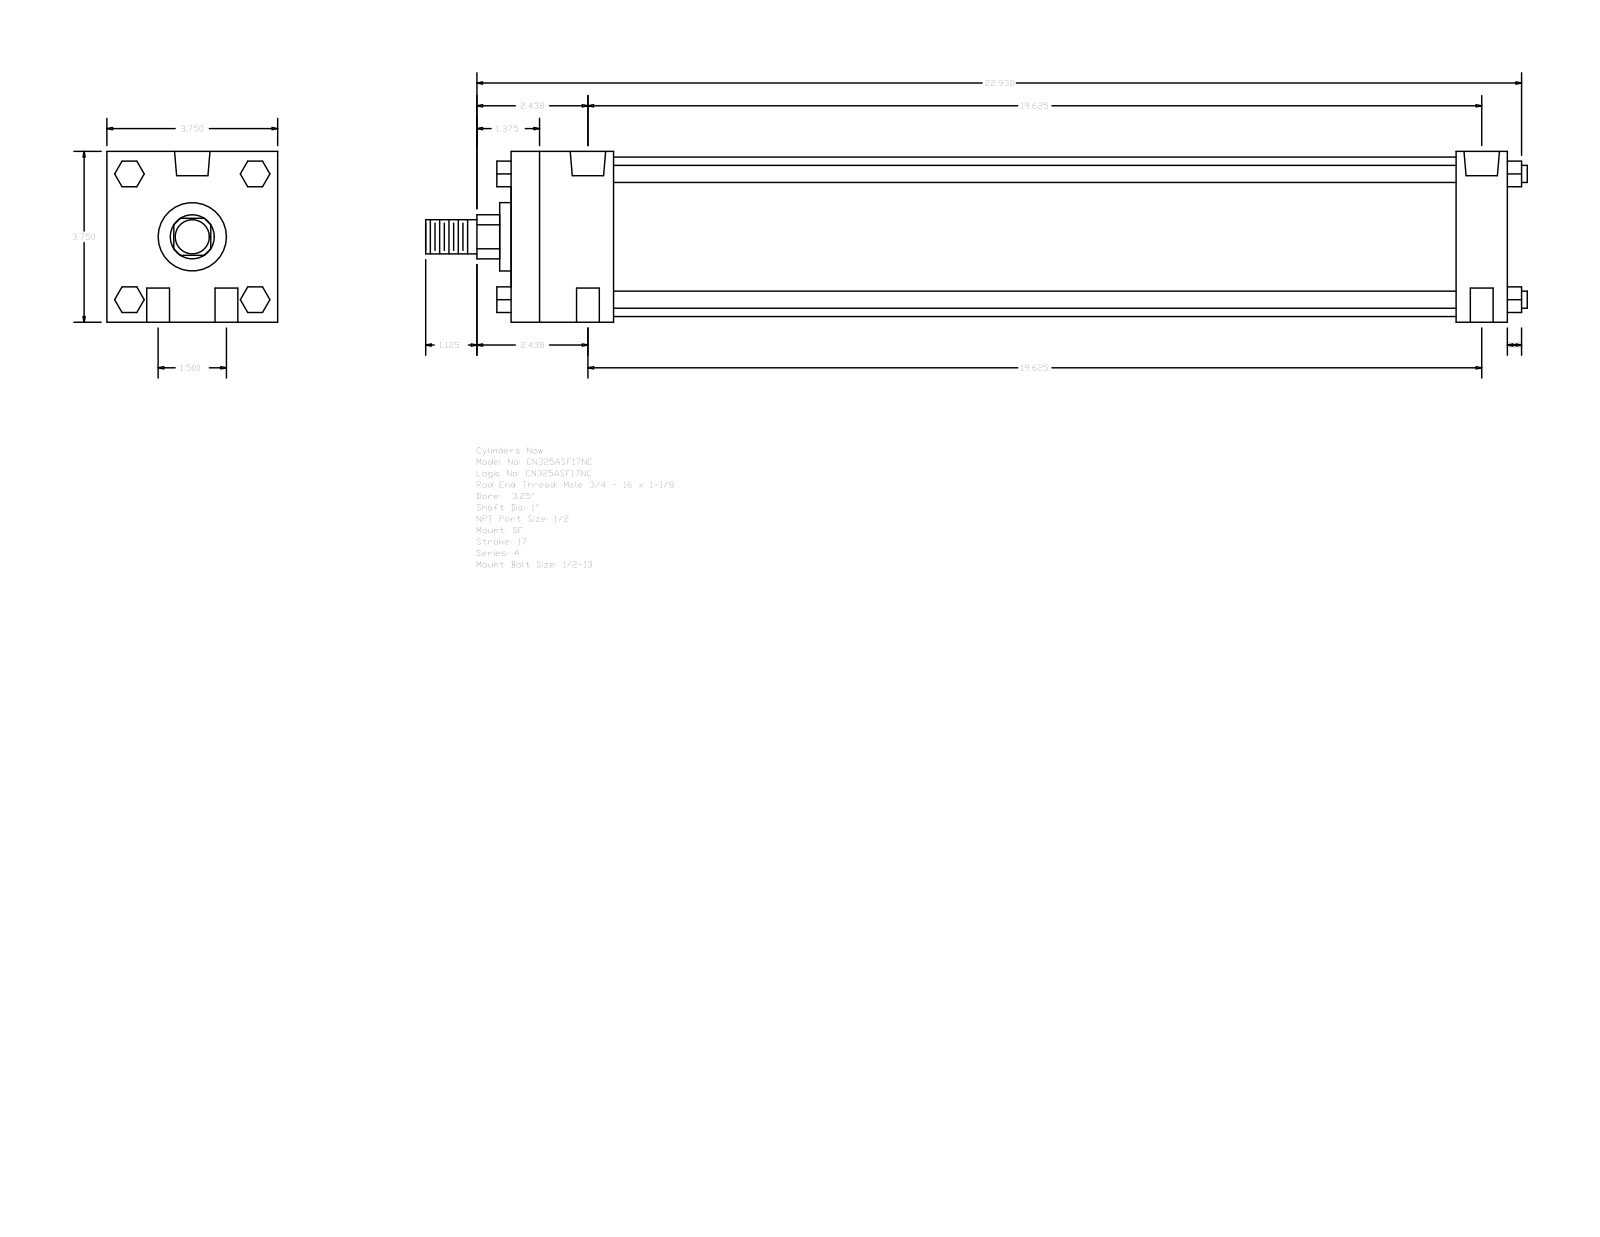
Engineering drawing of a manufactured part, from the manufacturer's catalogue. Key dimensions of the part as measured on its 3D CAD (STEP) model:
Part name (STEP PRODUCT): A_SF__0325_1
STEP written by: GSSL Pune (CONFIG_CONTROL_DESIGN)
Units: millimetres
Bodies: 0 solids, 124 faces (94 planar, 30 cylindrical, 0 other)
Overall size (bounding box): 614.36 × 95.25 × 95.25
Round holes (diameter × count): ⌀12.7 ×4, ⌀8.73 ×2, ⌀19.77 ×2
Round bosses / shafts (diameter × count): ⌀9.53 ×4, ⌀88.9 ×1, ⌀38.1 ×1, ⌀25.4 ×1, ⌀19.05 ×1
Partial cylindrical surfaces — rounded edges, fillets, slot ends (radius × count): R12.29 ×1
Main face-to-face distances: 95.24, 555.62, 28.57, 527.05, 57.15, 469.9, 498.47, 14.28, 35.05, 60.71
Hole centre spacings: 19.05, 498.84, 498.48, 38.1, 499.93, 492.12
